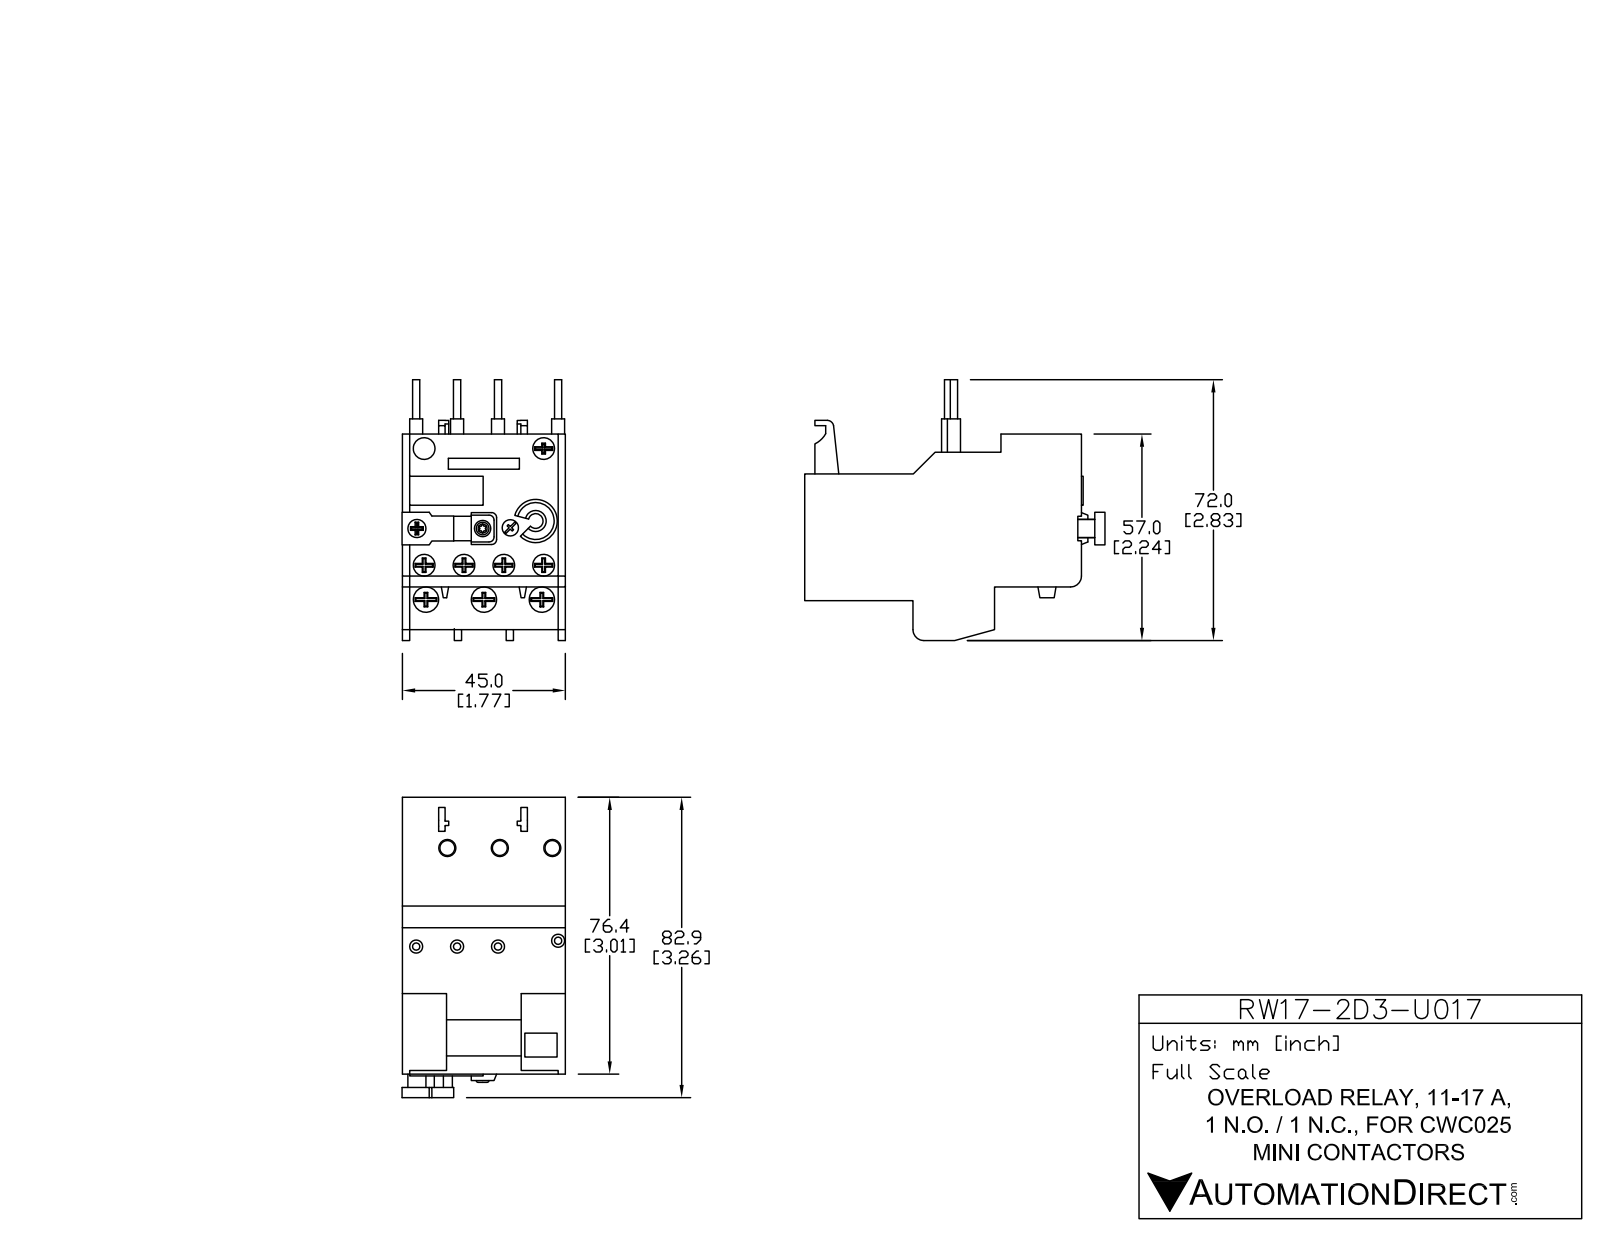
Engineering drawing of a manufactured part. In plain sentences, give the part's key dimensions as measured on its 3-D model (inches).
The part is named "RW17D-2D3-U017". Its 3-D file was written by "SolidWorks 2013 (AUTOMOTIVE_DESIGN)". It is 17 solids with 748 faces: 512 planar, 211 cylindrical and 25 other. Overall it measures 3.254 by 2.776 by 1.793 inches. Its volume is 7.772 cubic inches and its surface area 53.57 square inches. Round holes: 6 of diameter 0.236, 3 of diameter 0.157, 3 of diameter 0.276, 3 of diameter 0.295, 1 of diameter 0.177, 1 of diameter 0.187, 1 of diameter 0.21, 1 of diameter 0.217, 1 of diameter 0.41. Round bosses or shafts: 7 of diameter 0.217, 7 of diameter 0.118, 4 of diameter 0.069, 2 of diameter 0.22, 2 of diameter 0.128, 1 of diameter 0.253, 1 of diameter 0.242, 1 of diameter 0.187. Partial cylindrical surfaces (rounded edges, fillets, slot ends): 20 of radius 0.02, 12 of radius 0.01, 9 of radius 0.039, 6 of radius 0.178, 4 of radius 0.231, 4 of radius 0.309, 3 of radius 0.059, 2 of radius 0.049. The main face-to-face distances are 1.791, 0.059, 0.427, 0.433, 3.008, 1.378, 0.056, 2.952, 2.949, 0.236. The hole center spacings are 0.591, 0.337, 0.423, 1.181, 0.416, 0.467, 0.561, 0.841.
